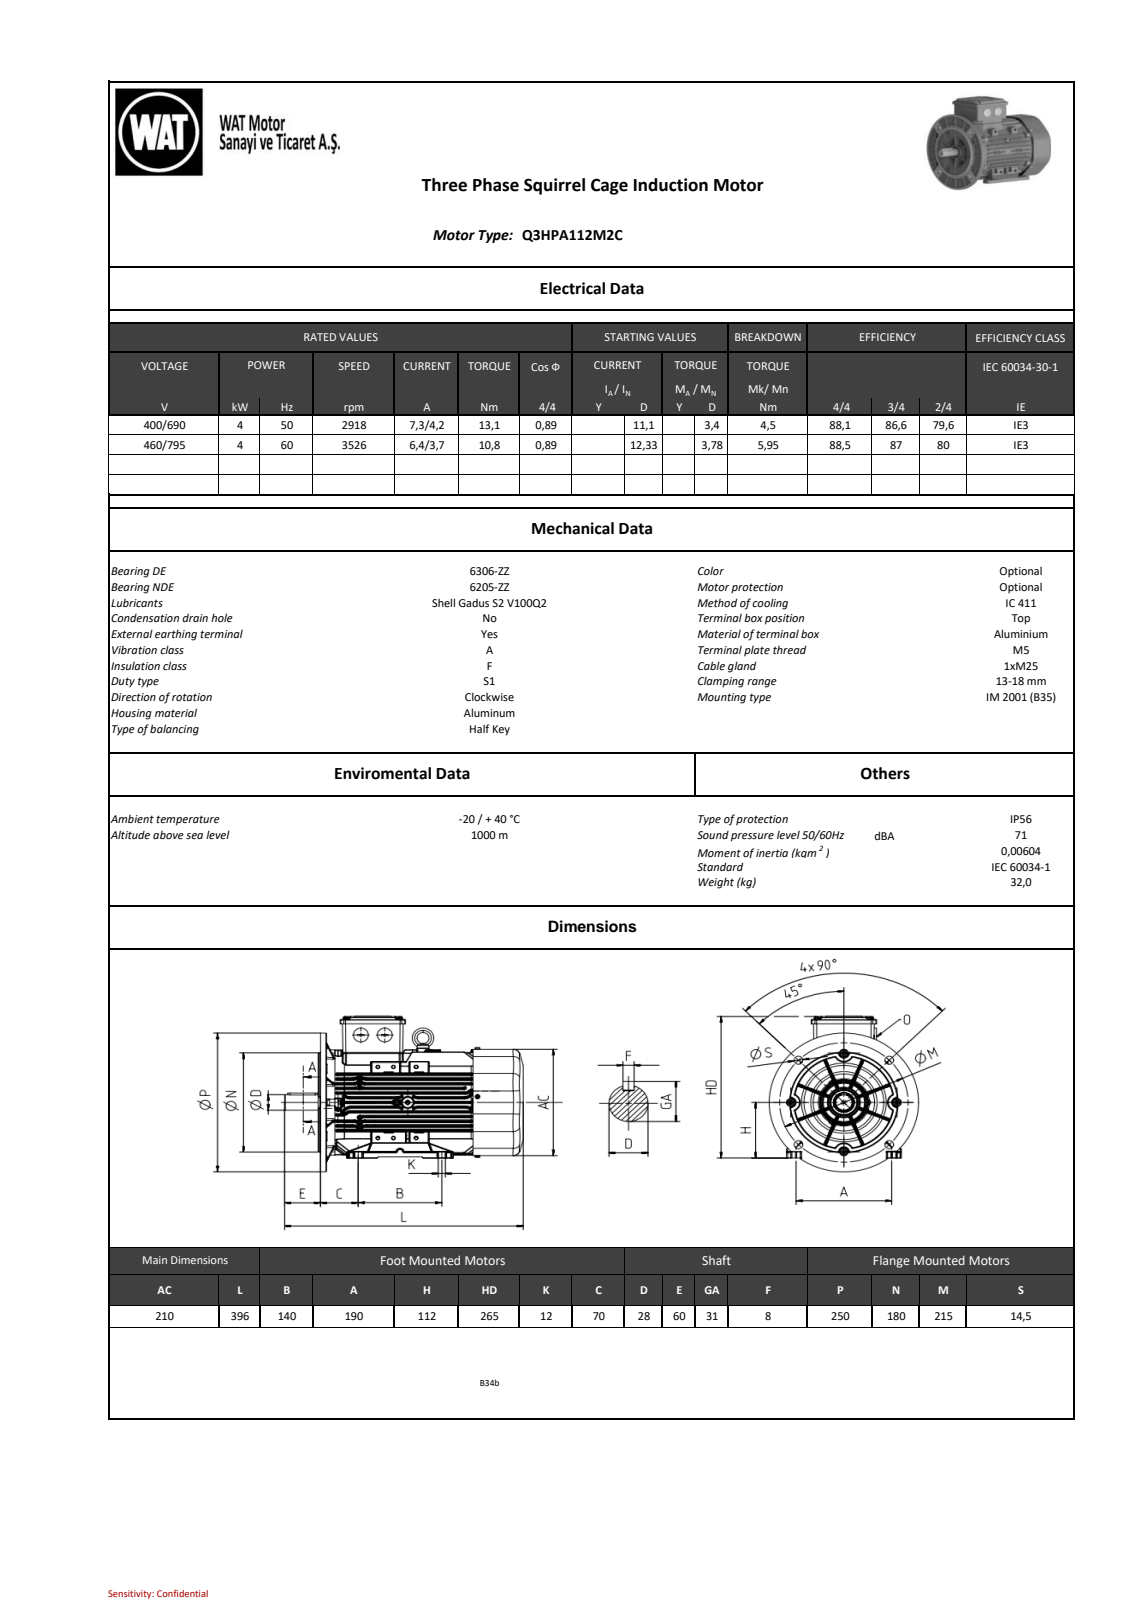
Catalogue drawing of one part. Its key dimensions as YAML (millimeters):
part_name: "QH series_ 112_B35_stp_objects"
step_written_by: "SIEMENS PLM Software NX2206.8101 (AUTOMOTIVE_DESIGN)"
units: millimeters
bodies: {solids: 0, faces: 7546, planar: 1607, cylindrical: 2819, other: 3120}
overall_size: [396, 287.37, 249.75]
round_holes:
  - {diameter: 4.6, count: 2}
  - {diameter: 8, count: 1}
  - {diameter: 8.5, count: 1}
round_bosses_or_shafts:
  - {diameter: 14.8, count: 4}
  - {diameter: 13, count: 4}
  - {diameter: 10, count: 4}
  - {diameter: 8, count: 4}
  - {diameter: 25, count: 2}
  - {diameter: 6, count: 2}
  - {diameter: 188, count: 1}
  - {diameter: 180, count: 1}
partial_cylinders:
  - {radius: 0.8, count: 608}
  - {radius: 2, count: 549}
  - {radius: 1, count: 434}
  - {radius: 0.5, count: 247}
  - {radius: 3, count: 167}
  - {radius: 4, count: 12}
  - {radius: 6, count: 12}
  - {radius: 10, count: 10}
face_to_face_distances: [1, 21.5, 10.99, 35.96, 99.54, 24.97, 90.43, 68.93, 30.61, 89.87]
